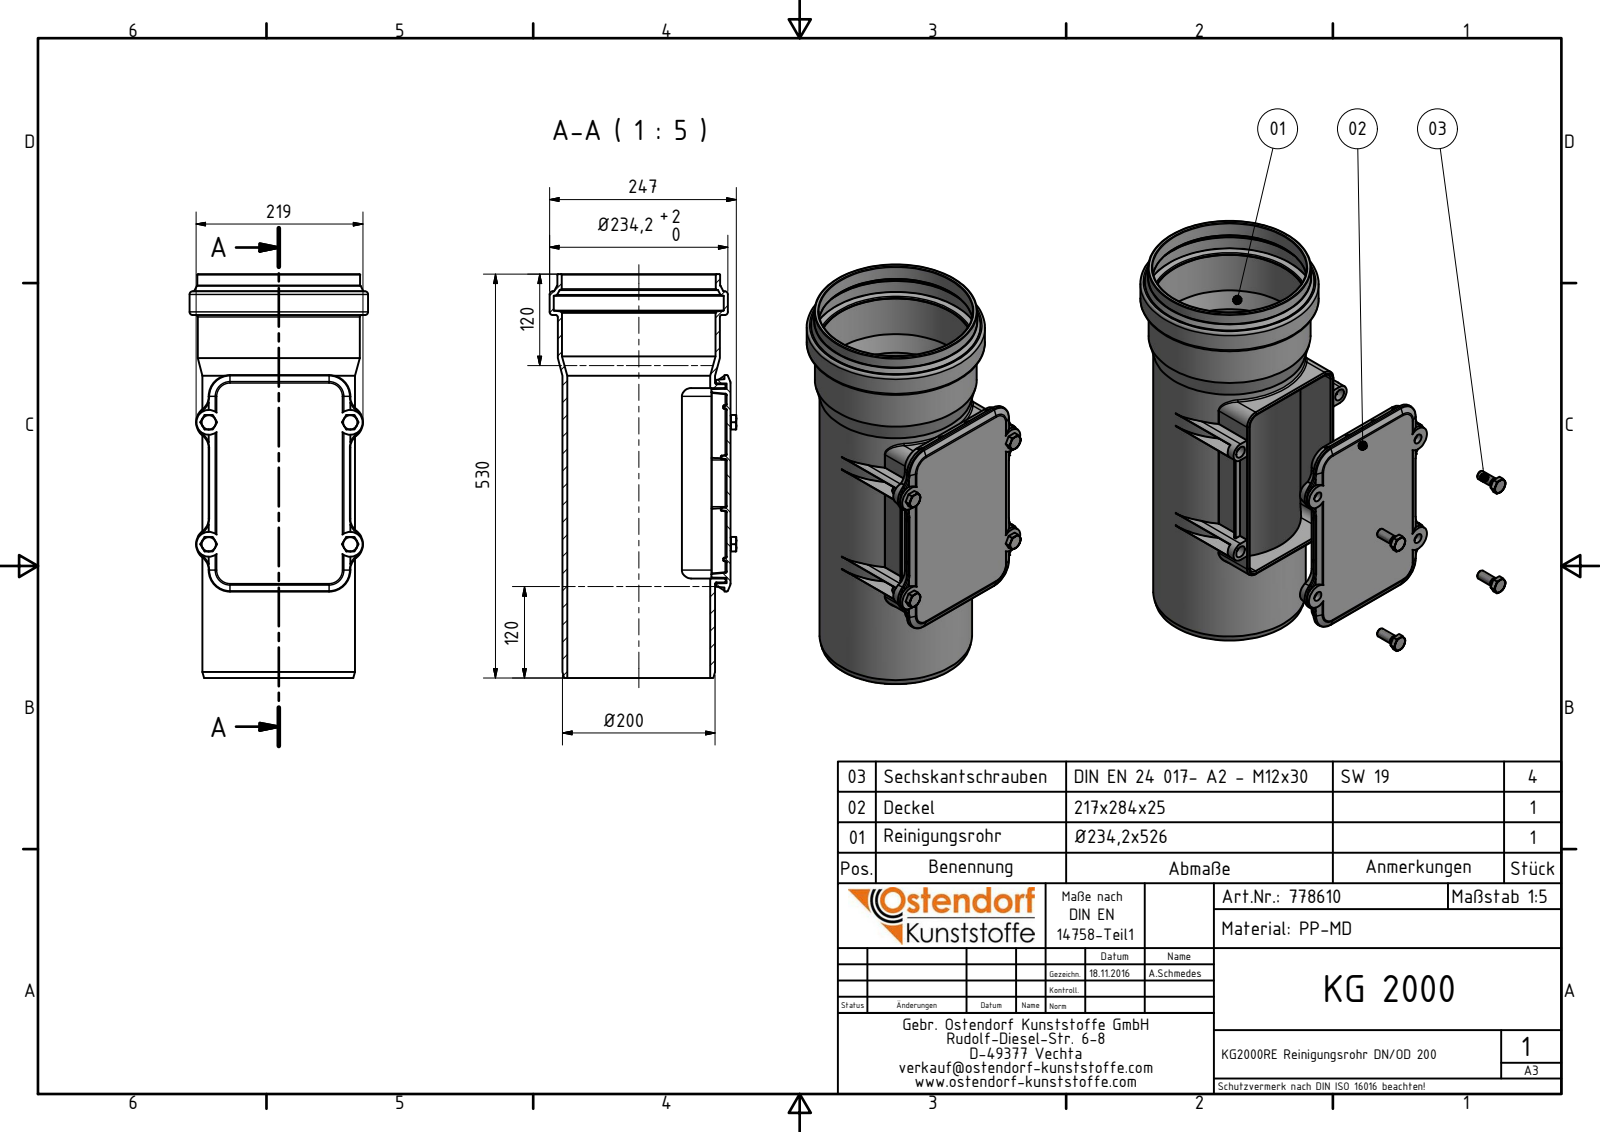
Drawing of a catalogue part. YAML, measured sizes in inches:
part_name: "778610 KG2000RE Reinigungsrohr DN_OD 200; 778610 KG2000RE Reinigungsrohr DN_OD 200 Deckel; DIN 933 - M12 x 30; 778610 KG2000RE Reinigungsrohr DN_OD 200 Zusammenbau"
step_written_by: "Autodesk Inventor 2016 (AUTOMOTIVE_DESIGN)"
units: inches
bodies: {solids: 6, faces: 1335, planar: 330, cylindrical: 449, other: 556}
overall_size: [20.866, 9.65, 9.22]
volume: 154.5
surface_area: 1391
round_holes:
  - {diameter: 0.512, count: 4}
  - {diameter: 0.63, count: 4}
  - {diameter: 7.398, count: 1}
  - {diameter: 7.933, count: 1}
  - {diameter: 7.972, count: 1}
  - {diameter: 8.78, count: 1}
round_bosses_or_shafts:
  - {diameter: 0.677, count: 4}
  - {diameter: 0.472, count: 4}
  - {diameter: 0.435, count: 4}
  - {diameter: 9.22, count: 1}
  - {diameter: 8.413, count: 1}
  - {diameter: 8.374, count: 1}
  - {diameter: 7.886, count: 1}
partial_cylinders:
  - {radius: 0.039, count: 104}
  - {radius: 0.02, count: 67}
  - {radius: 0.079, count: 32}
  - {radius: 0.197, count: 14}
  - {radius: 0.787, count: 8}
  - {radius: 0.059, count: 4}
  - {radius: 0.134, count: 4}
  - {radius: 0.431, count: 4}
face_to_face_distances: [0.201, 0.197, 6.106, 0.118, 5.906, 6.307, 0.787, 0.315, 6.299, 0.748]
hole_center_spacings: [6.299, 0.079, 6.3, 7.244, 7.323, 9.6, 9.659]
